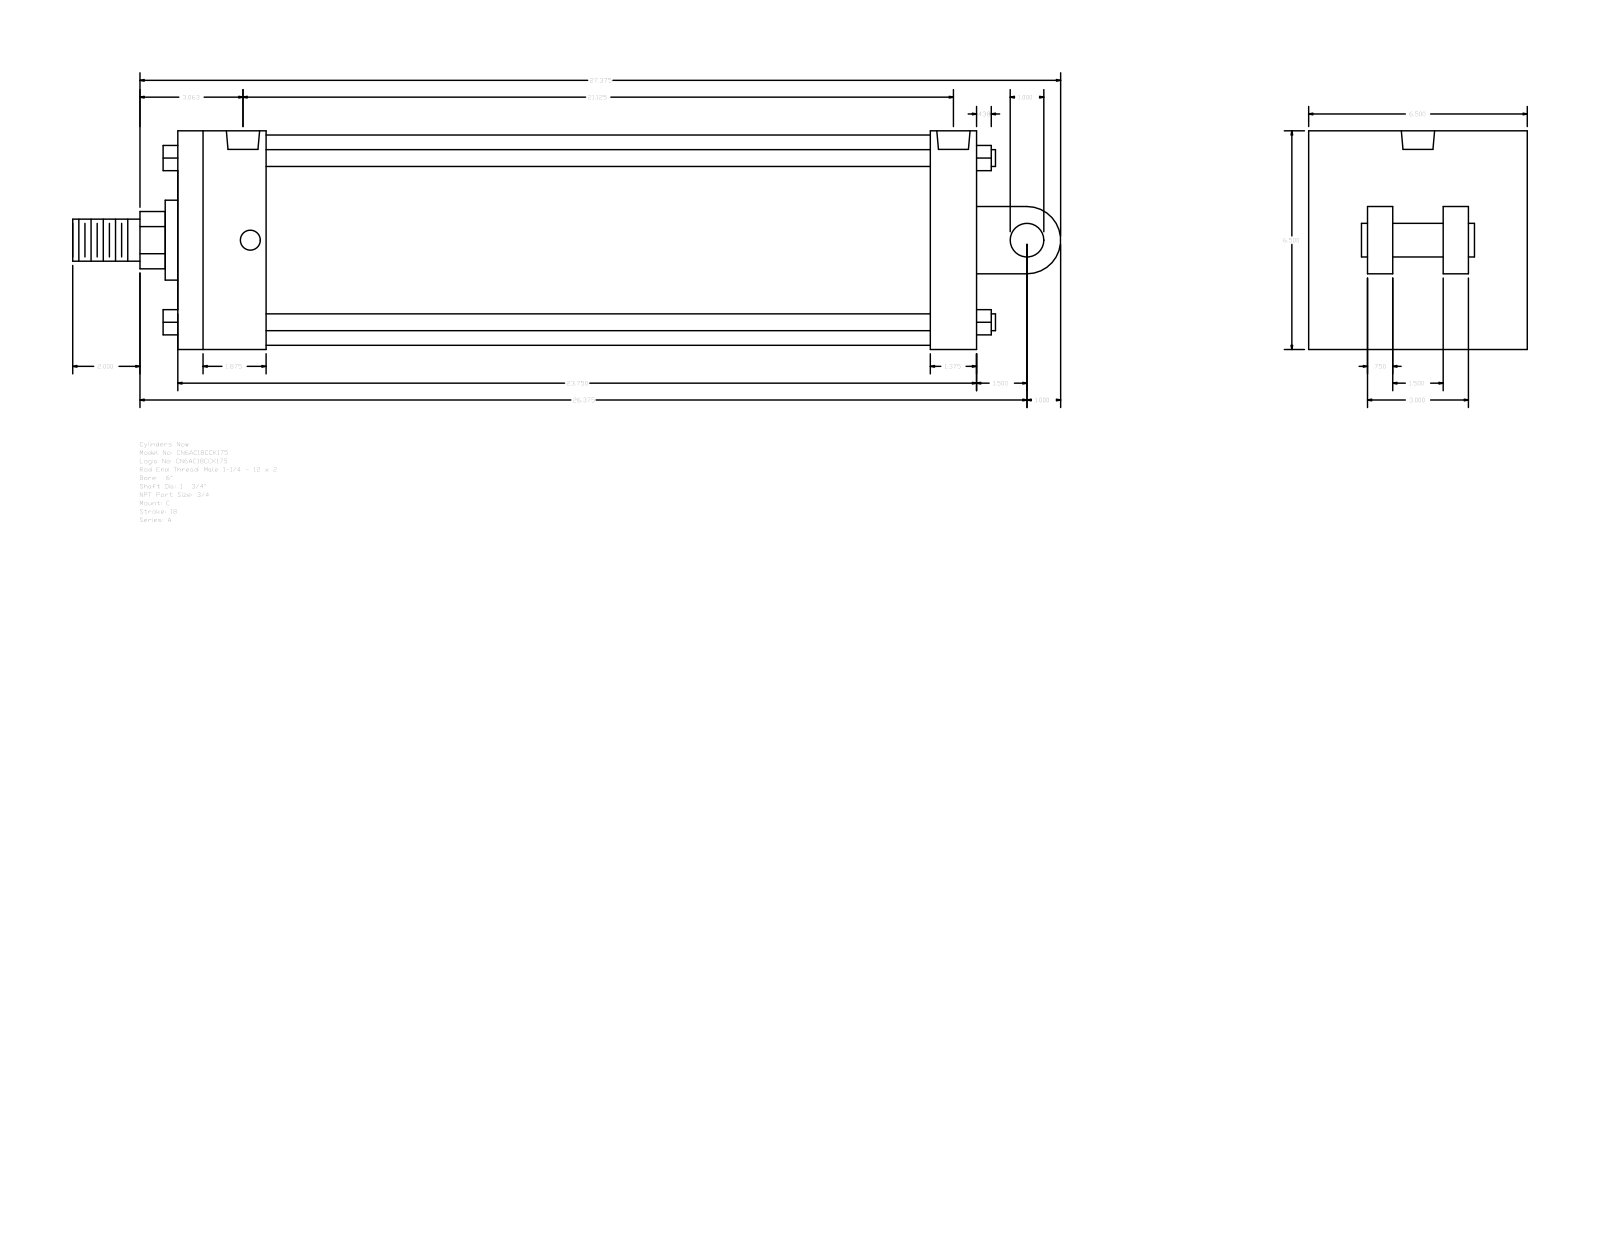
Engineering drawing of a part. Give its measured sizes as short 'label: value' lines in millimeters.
name: A_C__0600_1.75
written by: GSSL Pune (CONFIG_CONTROL_DESIGN)
unit: mm
bodies: 0 solids, 135 faces (102 planar, 33 cylindrical, 0 other)
size: 746.12 × 165.1 × 165.1
holes: 4× ⌀15.08, 2× ⌀25.12
bosses: 4× ⌀12.7, 1× ⌀158.75, 1× ⌀60.33, 1× ⌀44.45, 1× ⌀31.75, 1× ⌀25.4
rounds: 1× R21.63, 1× R25.4
face distances: 165.1, 603.26, 19.05, 57.15, 66.68, 536.58, 568.33, 501.65, 34.93, 63.5
hole spacings: 5.56, 525.45, 531.01, 536.57
